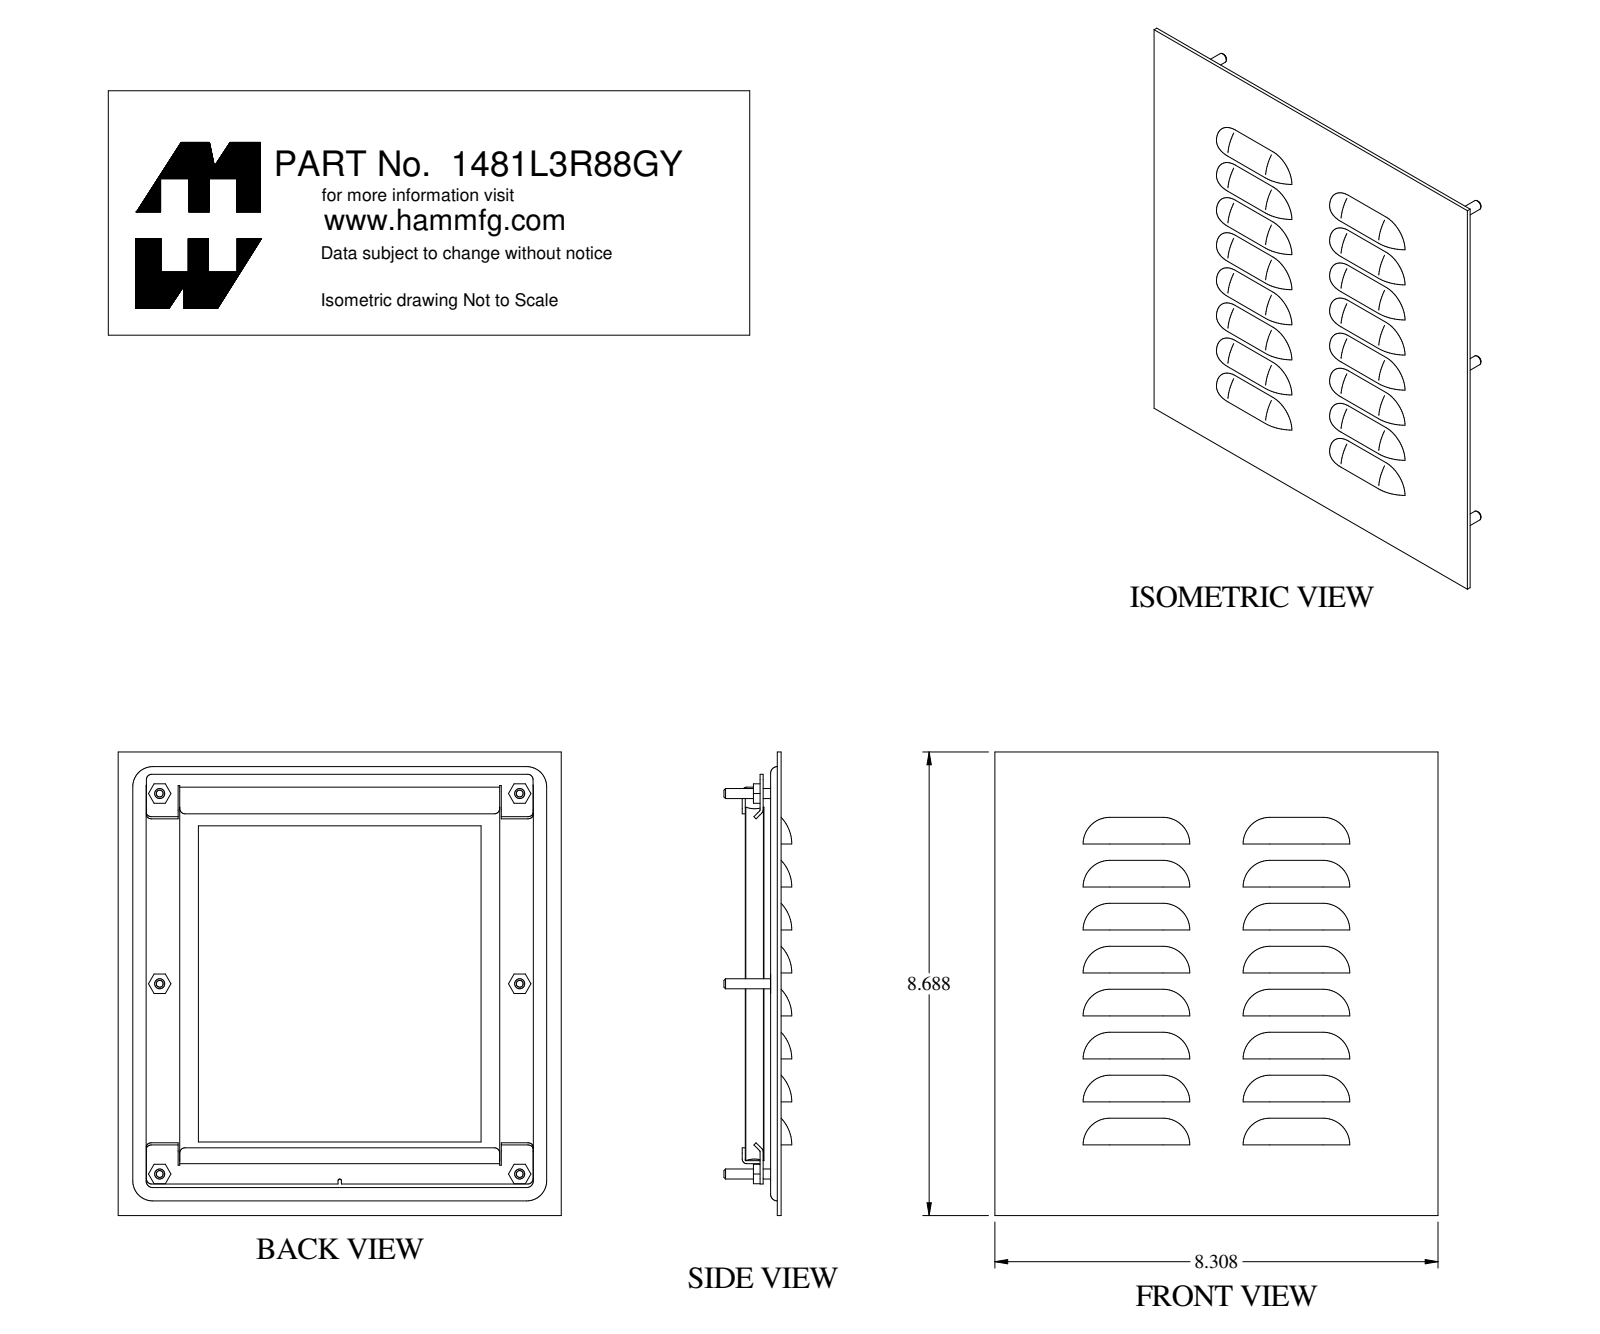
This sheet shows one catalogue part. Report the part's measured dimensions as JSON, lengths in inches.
{"part_name": "1481L3R88GY", "step_written_by": "SolidWorks 2021 (AUTOMOTIVE_DESIGN)", "units": "inches", "bodies": {"solids": 17, "faces": 400, "planar": 189, "cylindrical": 123, "other": 88}, "overall_size": [8.688, 8.308, 1.272], "volume_in3": 17.67, "surface_area_in2": 316.7, "round_holes": [[0.156, 6], [0.22, 4]], "round_bosses_or_shafts": [[0.25, 6], [0.188, 6]], "partial_cylinders_radius": [[0.1, 12], [0.653, 8], [0.725, 8], [0.029, 6], [0.086, 6], [0.125, 4], [0.126, 4], [0.374, 4]], "face_to_face_distances": [0.072, 0.3, 0.25, 0.372, 0.622, 0.55, 0.05, 0.322, 0.672, 0.6], "hole_center_spacings": [3.565, 7.13, 7.633, 6.75, 6.75, 7.633, 9.818, 9.819]}
